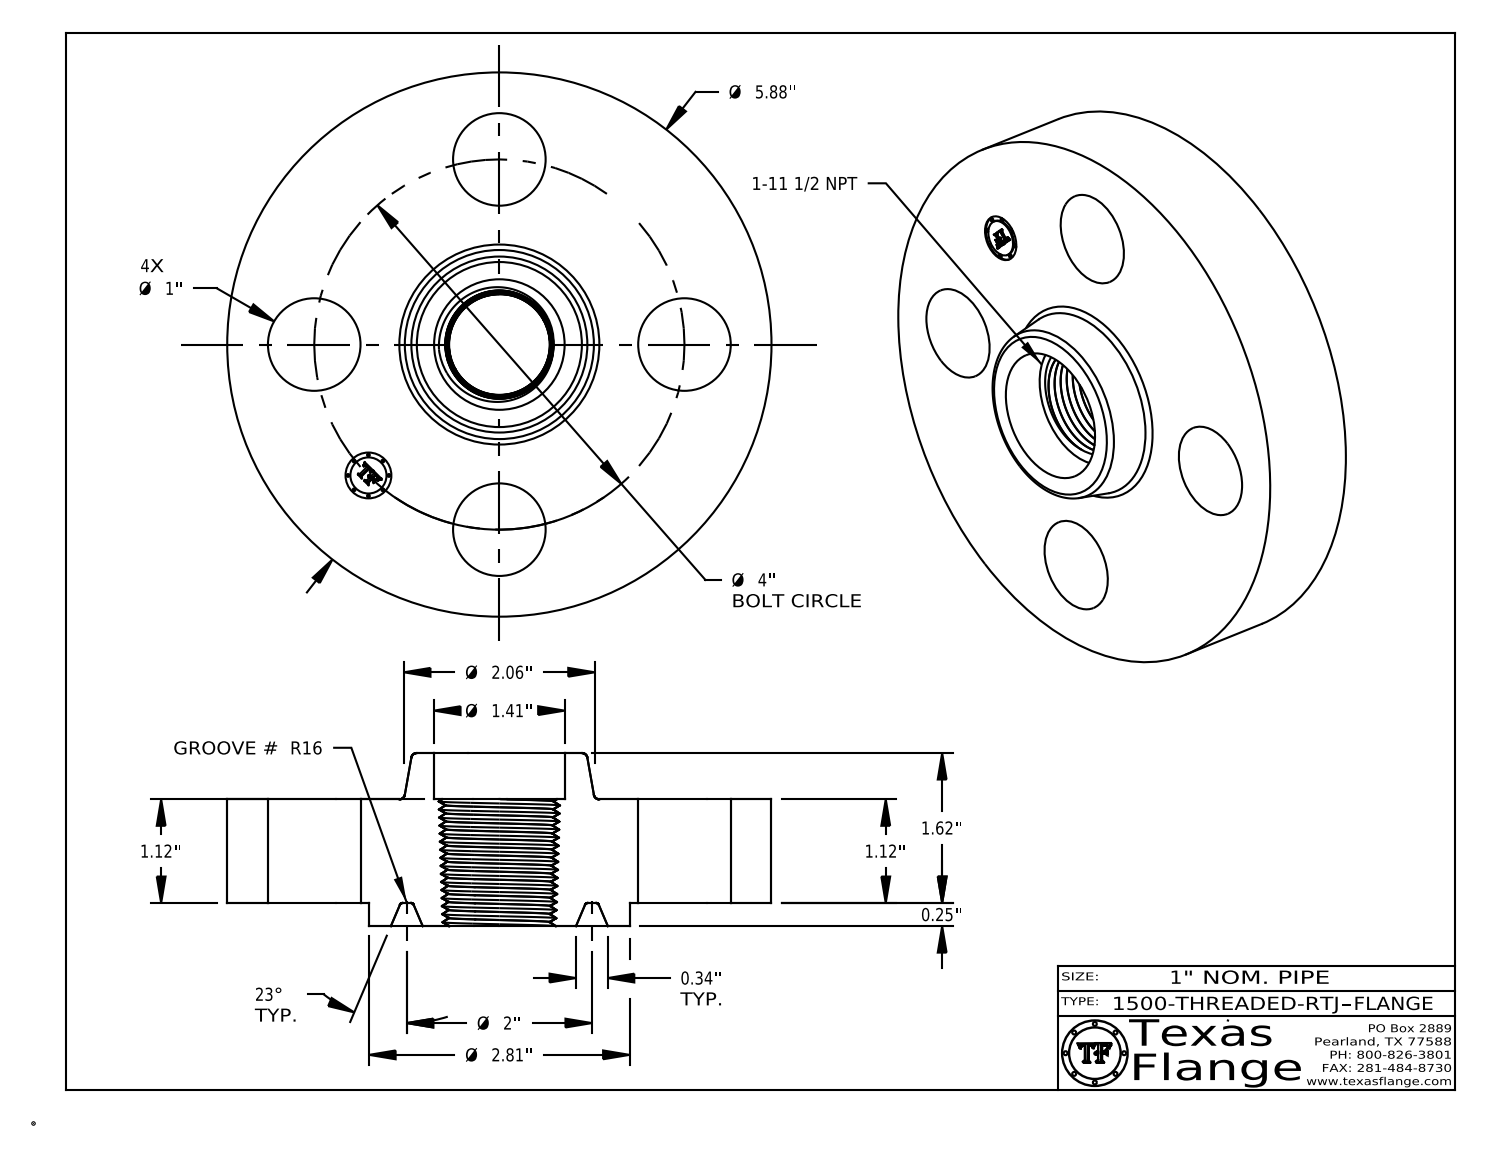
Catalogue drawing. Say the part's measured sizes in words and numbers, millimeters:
The part is named "1500-THREADED-RTJ". Its 3-D file was written by "CATIA V5 STEP AP214 (AUTOMOTIVE_DESIGN)". It is 1 solid with 583 faces: 372 planar, 34 cylindrical and 177 other. Overall it measures 149.4 by 149.4 by 47.5 millimeters. Its volume is 447 000 cubic millimeters and its surface area 63 960 square millimeters. Round holes: 4 of diameter 25.4, 1 of diameter 12.6, 1 of diameter 35.8. Round bosses or shafts: 8 of diameter 0.8, 1 of diameter 149.4, 1 of diameter 71.5, 1 of diameter 9.9. The main face-to-face distances are 28.4, 6.4, 34.8, 47.5, 41.1, 12.7, 0.4, 34.4, 28.1, 13.1. The hole center spacings are 50.8, 71.8, 38.9, 93.9, 101.6.
